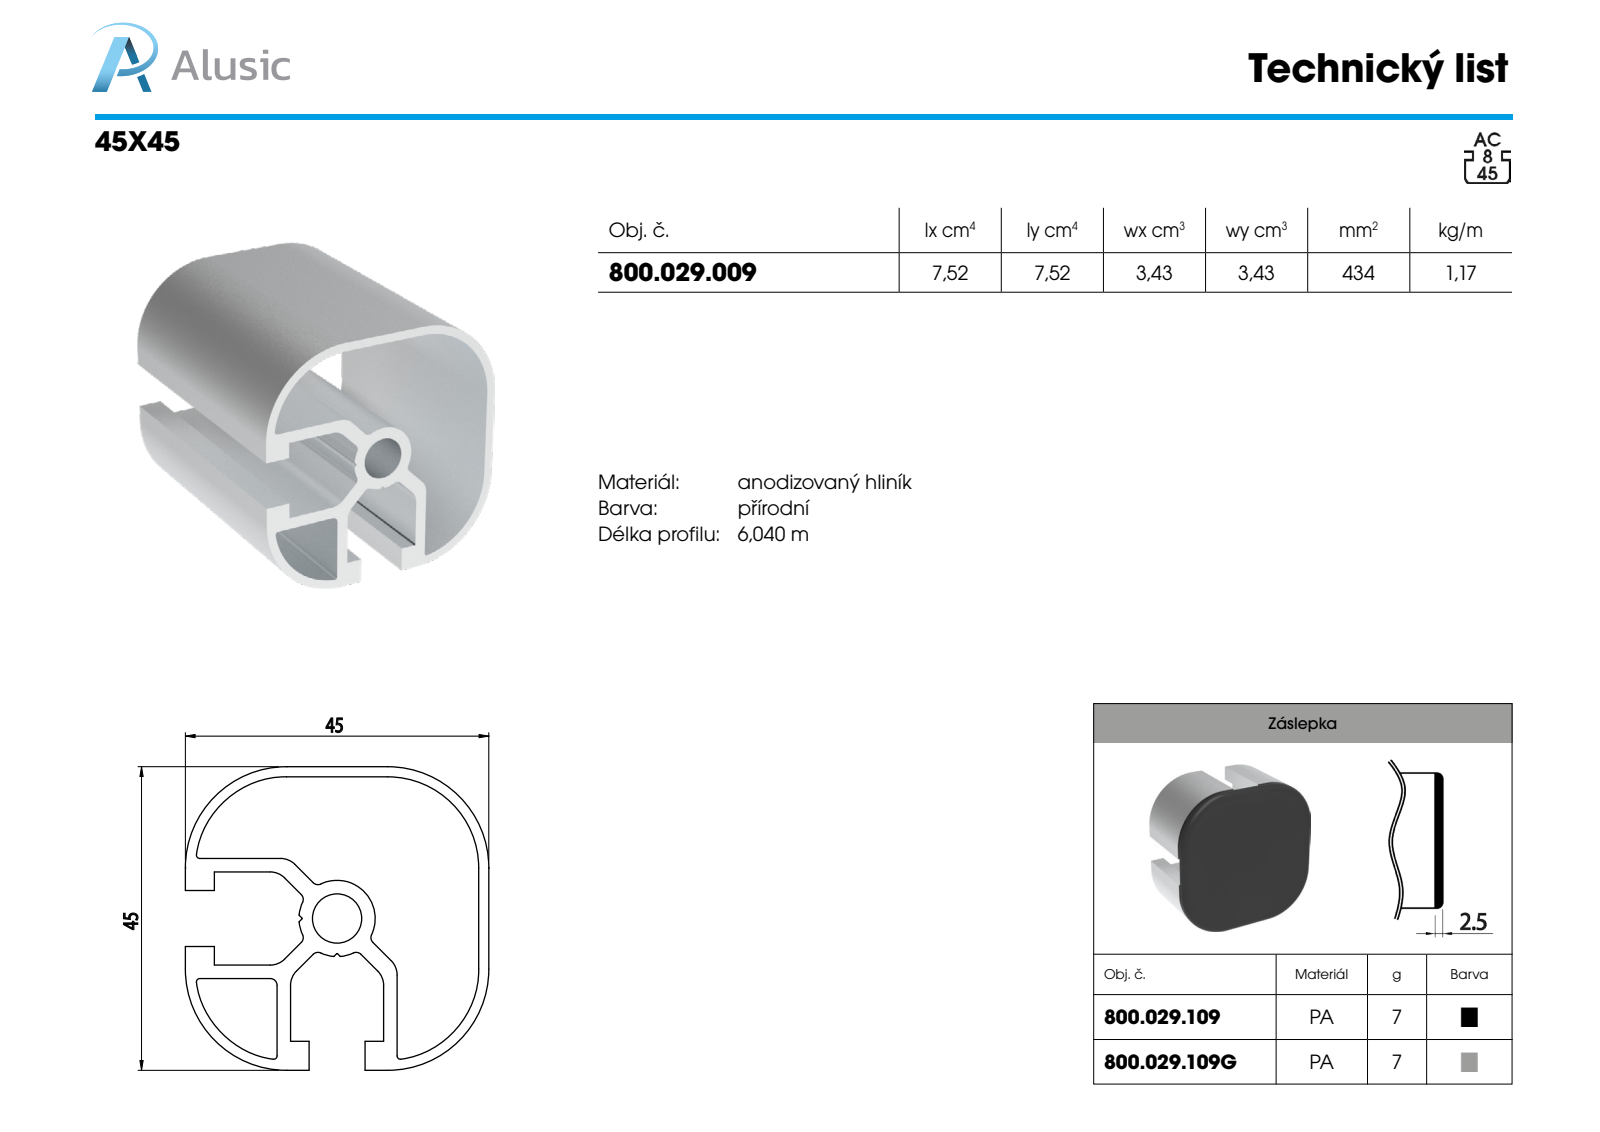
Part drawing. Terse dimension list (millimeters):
name: 800.029.009
written by: SolidWorks 2018 (AUTOMOTIVE_DESIGN)
unit: mm
bodies: 1 solid, 78 faces (36 planar, 42 cylindrical, 0 other)
size: 100 × 45 × 45
volume: 43 410 mm³; area: 45 510 mm²
holes: 1× ⌀7.3
rounds: 7× R1, 6× R0.1, 6× R3, 4× R0.5, 4× R13.5, 4× R15, 1× R5.65
face distances: 13.6, 31.4, 2, 15.8, 1.5, 29.4, 15.6, 12.1, 17.8, 29.9
